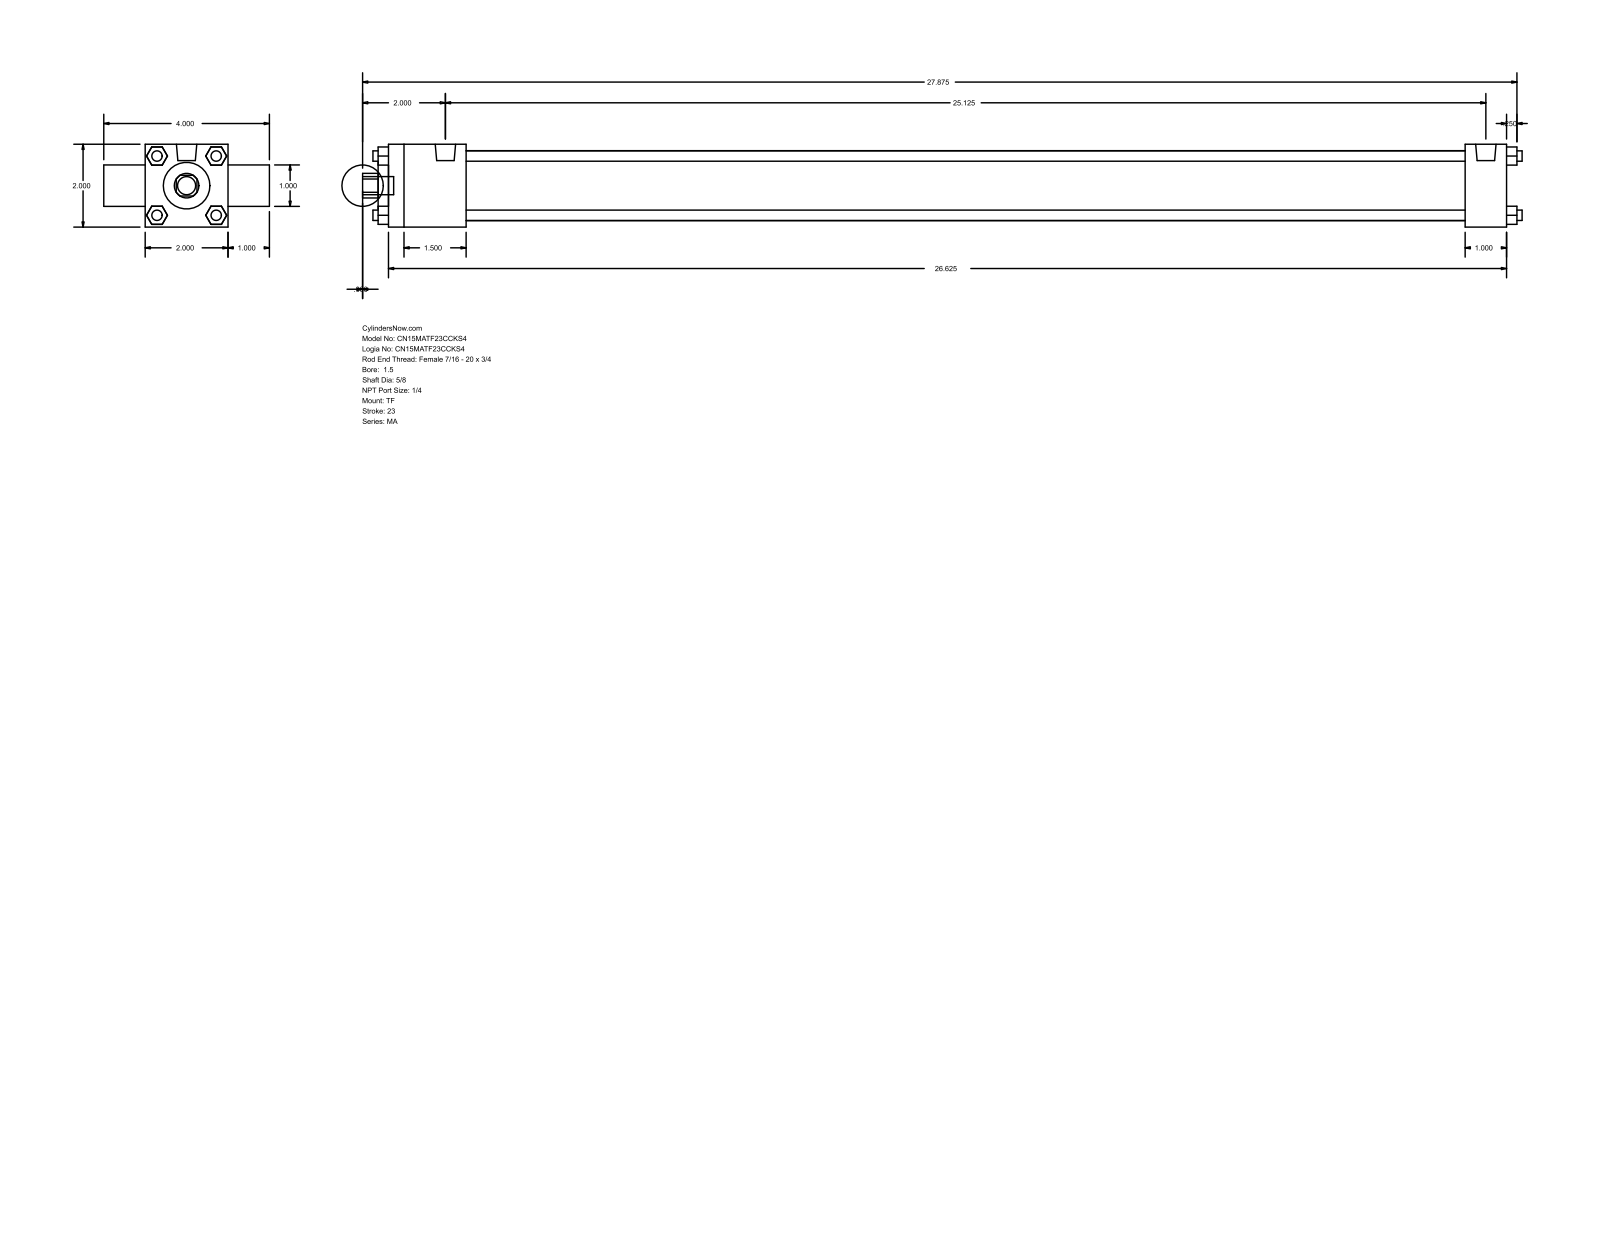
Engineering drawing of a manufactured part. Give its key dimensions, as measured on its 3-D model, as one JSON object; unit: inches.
{"part_name": "MA_TF__0150_0.625", "step_written_by": "GSSL Pune (CONFIG_CONTROL_DESIGN)", "units": "inches", "bodies": {"solids": 0, "faces": 120, "planar": 92, "cylindrical": 28, "other": 0}, "overall_size": [28, 4, 2], "round_holes": [[0.625, 1], [1, 1], [1.125, 1], [1.69, 1]], "round_bosses_or_shafts": [[0.25, 4], [0.313, 3], [0.492, 2], [0.437, 1]], "partial_cylinders_radius": [[0.297, 1]], "face_to_face_distances": [2, 1, 27, 0.25, 27.25, 3, 1.875, 26, 24.125, 25.125]}
